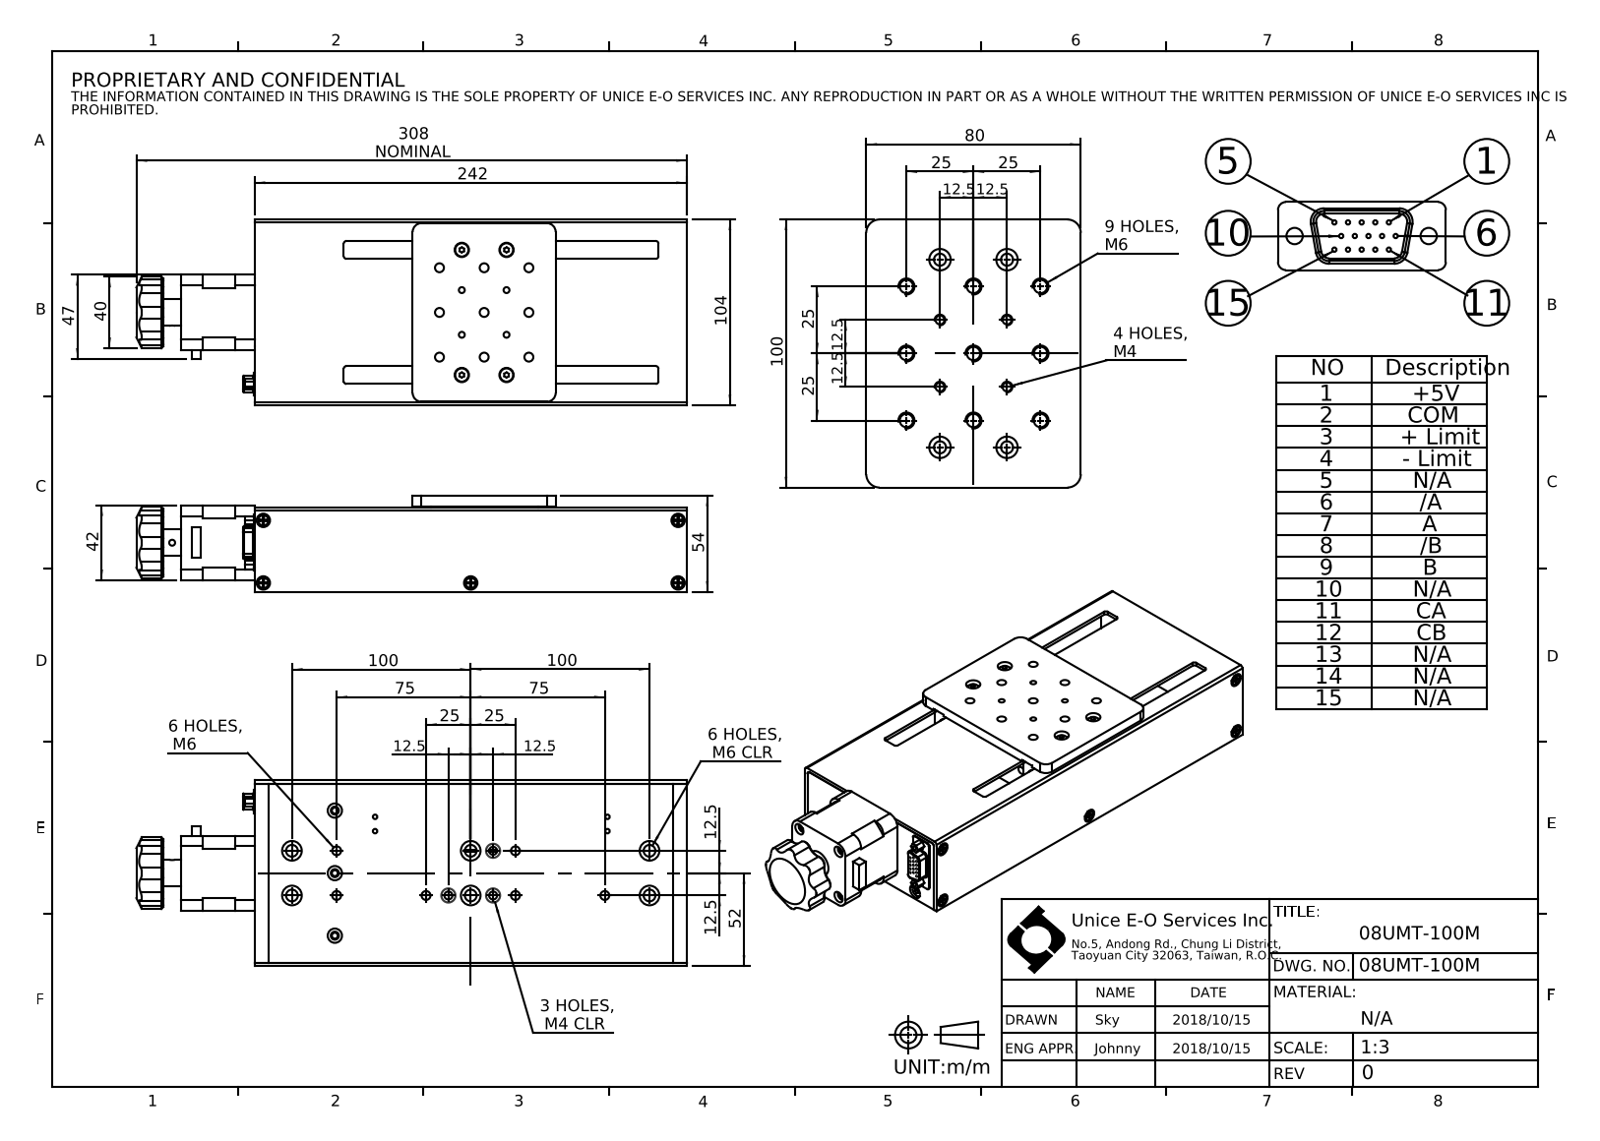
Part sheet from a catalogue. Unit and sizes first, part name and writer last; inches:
Units: inches
Overall size (bounding box): 12.126 × 4.094 × 2.126
Round holes (diameter × count): ⌀0.031 ×15, ⌀0.197 ×15, ⌀0.315 ×10, ⌀0.098 ×6, ⌀0.26 ×6, ⌀0.433 ×6, ⌀0.177 ×5, ⌀0.13 ×4, ⌀0.256 ×4, ⌀0.591 ×1, ⌀0.827 ×1
Round bosses / shafts (diameter × count): ⌀0.228 ×5
Partial cylindrical surfaces — rounded edges, fillets, slot ends (radius × count): R0.02 ×21, R0.059 ×15, R0.157 ×8, R0.292 ×8, R0.079 ×6, R0.197 ×4, R0.236 ×4, R0.118 ×1
Main face-to-face distances: 0.079, 4.016, 0.394, 1.85, 1.772, 1.378, 1.457, 4.094, 3.937, 0.276
Hole centre spacings: 0.112, 0.984, 0.18, 0.2, 0.1, 0.269, 1.392, 0.224
Bodies: 0 solids, 685 faces (293 planar, 257 cylindrical, 135 other)
Part name (STEP PRODUCT): 08UMT-100M
STEP written by: SolidWorks 2016 (AUTOMOTIVE_DESIGN)
